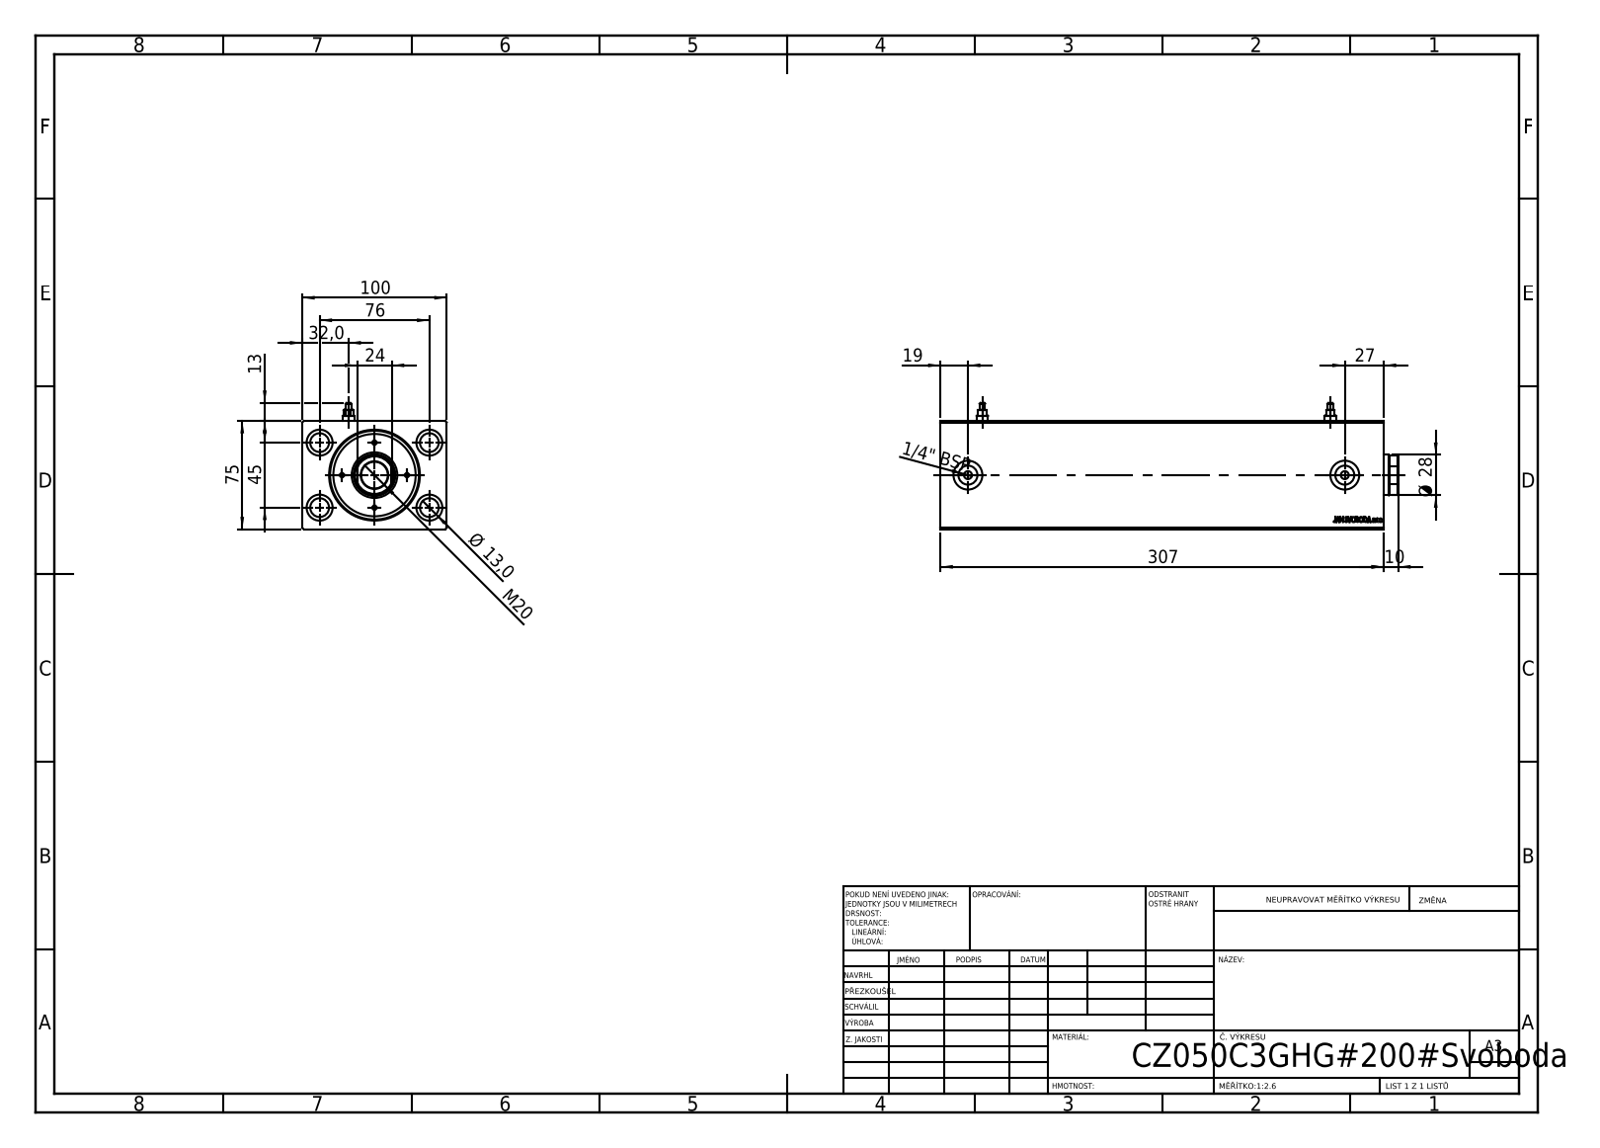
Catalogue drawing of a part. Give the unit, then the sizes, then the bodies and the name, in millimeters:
Units: millimetres
Overall size (bounding box): 307 × 100 × 75
Round holes (diameter × count): ⌀13 ×4, ⌀18 ×4, ⌀5.5 ×2, ⌀8 ×2, ⌀13.16 ×2, ⌀20 ×2, ⌀36 ×1, ⌀50 ×1, ⌀61.5 ×1
Main face-to-face distances: 75, 100, 307, 289.2, 17.8, 306.8, 17.6, 10, 279.2, 296.8
Hole centre spacings: 44.16, 45, 76, 88.32, 241, 261
Volume: 1 546 000 mm³ · Surface area: 219 419 mm²
Bodies: 1 solid, 825 faces (397 planar, 46 cylindrical, 382 other)
STEP written by: SolidWorks 2019 (CONFIG_CONTROL_DESIGN)
